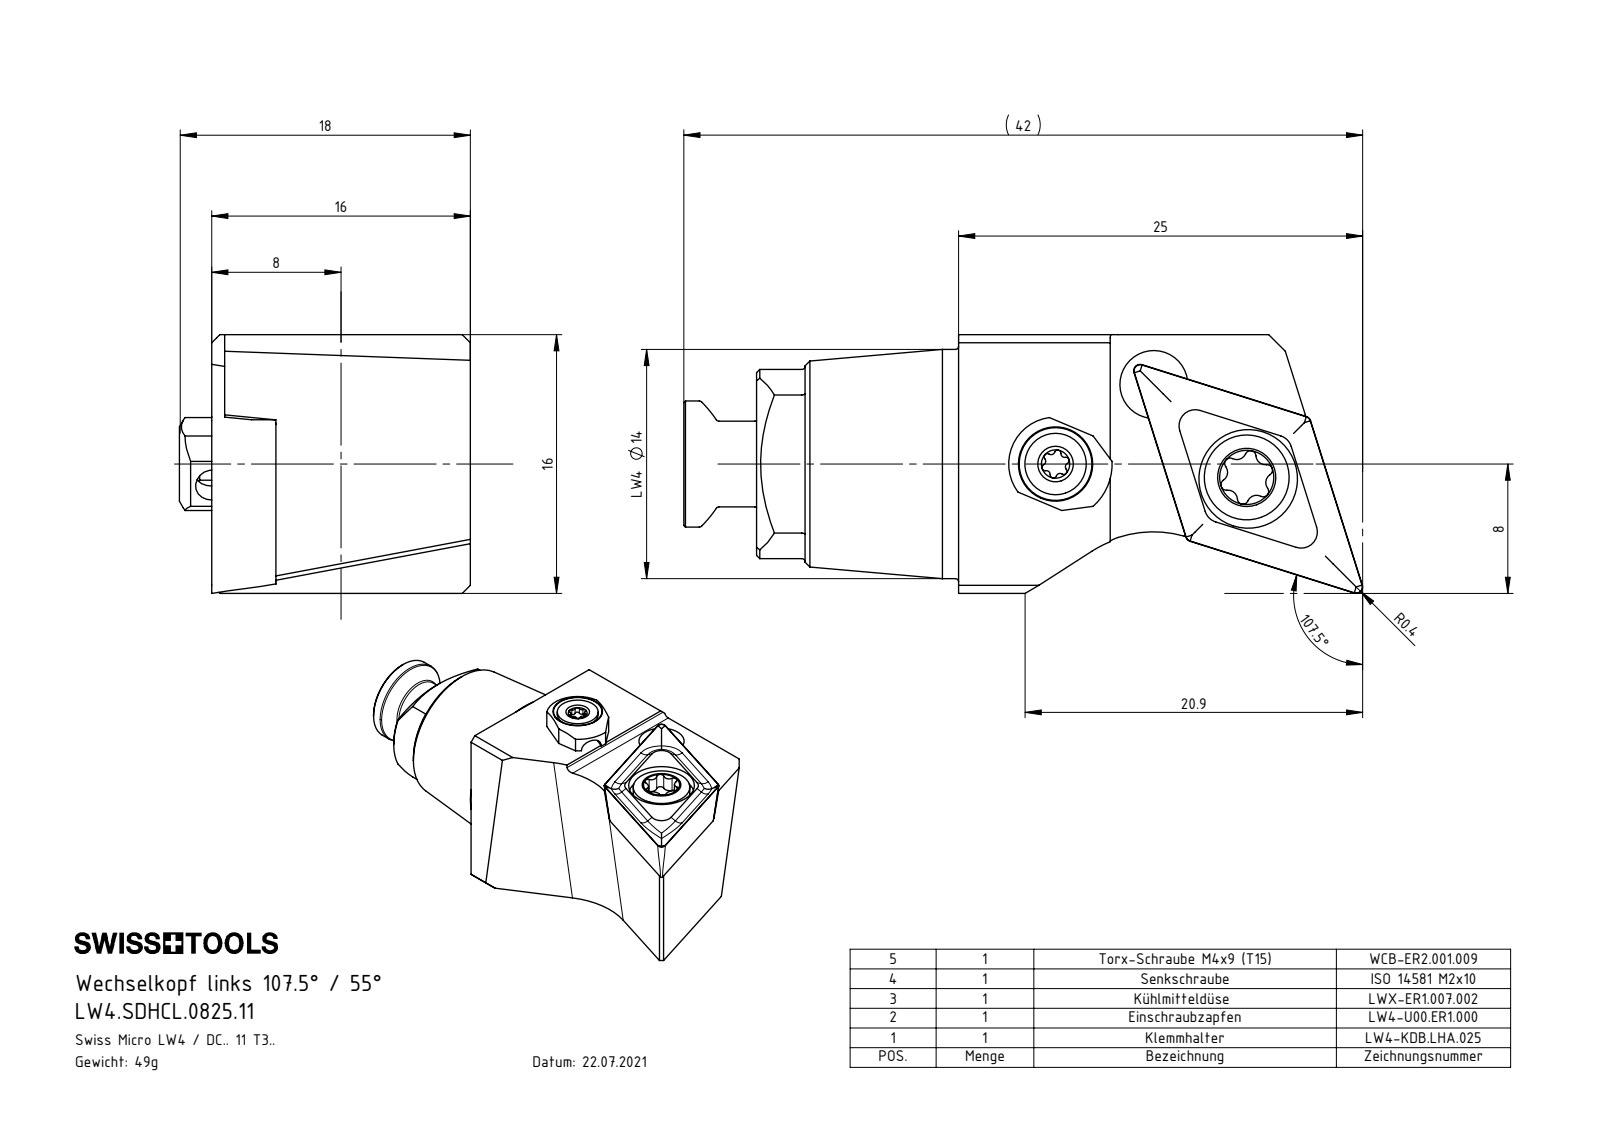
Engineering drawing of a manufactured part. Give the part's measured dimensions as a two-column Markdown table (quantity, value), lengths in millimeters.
| quantity | value |
| --- | --- |
| part name | DCMT11T304; WCB-ER2.001.009_A; LW4.SDHCL.0825.11; LW4-KDB.LHA.025_A (+3 more) |
| STEP written by | SolidWorks 2022 (CONFIG_CONTROL_DESIGN) |
| units | millimeters |
| bodies | 6 solids, 263 faces (70 planar, 82 cylindrical, 111 other) |
| overall size | 42.01 × 18 × 16 |
| volume | 6 049 mm³ |
| surface area | 3 792 mm² |
| round holes (diameter × count) | 2 × 2, 1.6 × 1, 2.5 × 1, 3 × 1, 3.3 × 1, 4.2 × 1, 4.4 × 1, 5.5 × 1, 6.1 × 1 |
| round bosses / shafts (diameter × count) | 14.17 × 1, 7.7 × 1, 6 × 1, 5.3 × 1, 5.25 × 1, 5 × 1, 4 × 1, 3.8 × 1 |
| partial cylindrical surfaces (radius × count) | 0.2 × 8, 0.24 × 6, 0.34 × 6, 0.59 × 6, 0.5 × 1, 1 × 1, 2.9 × 1, 3.5 × 1 |
| main face-to-face distances | 16, 12.03, 3.97, 7.5, 15.2, 3.17, 0.8, 2, 3, 12.5 |
| hole center spacings | 7.51, 8.13, 8.26, 11.46, 11.56 |
